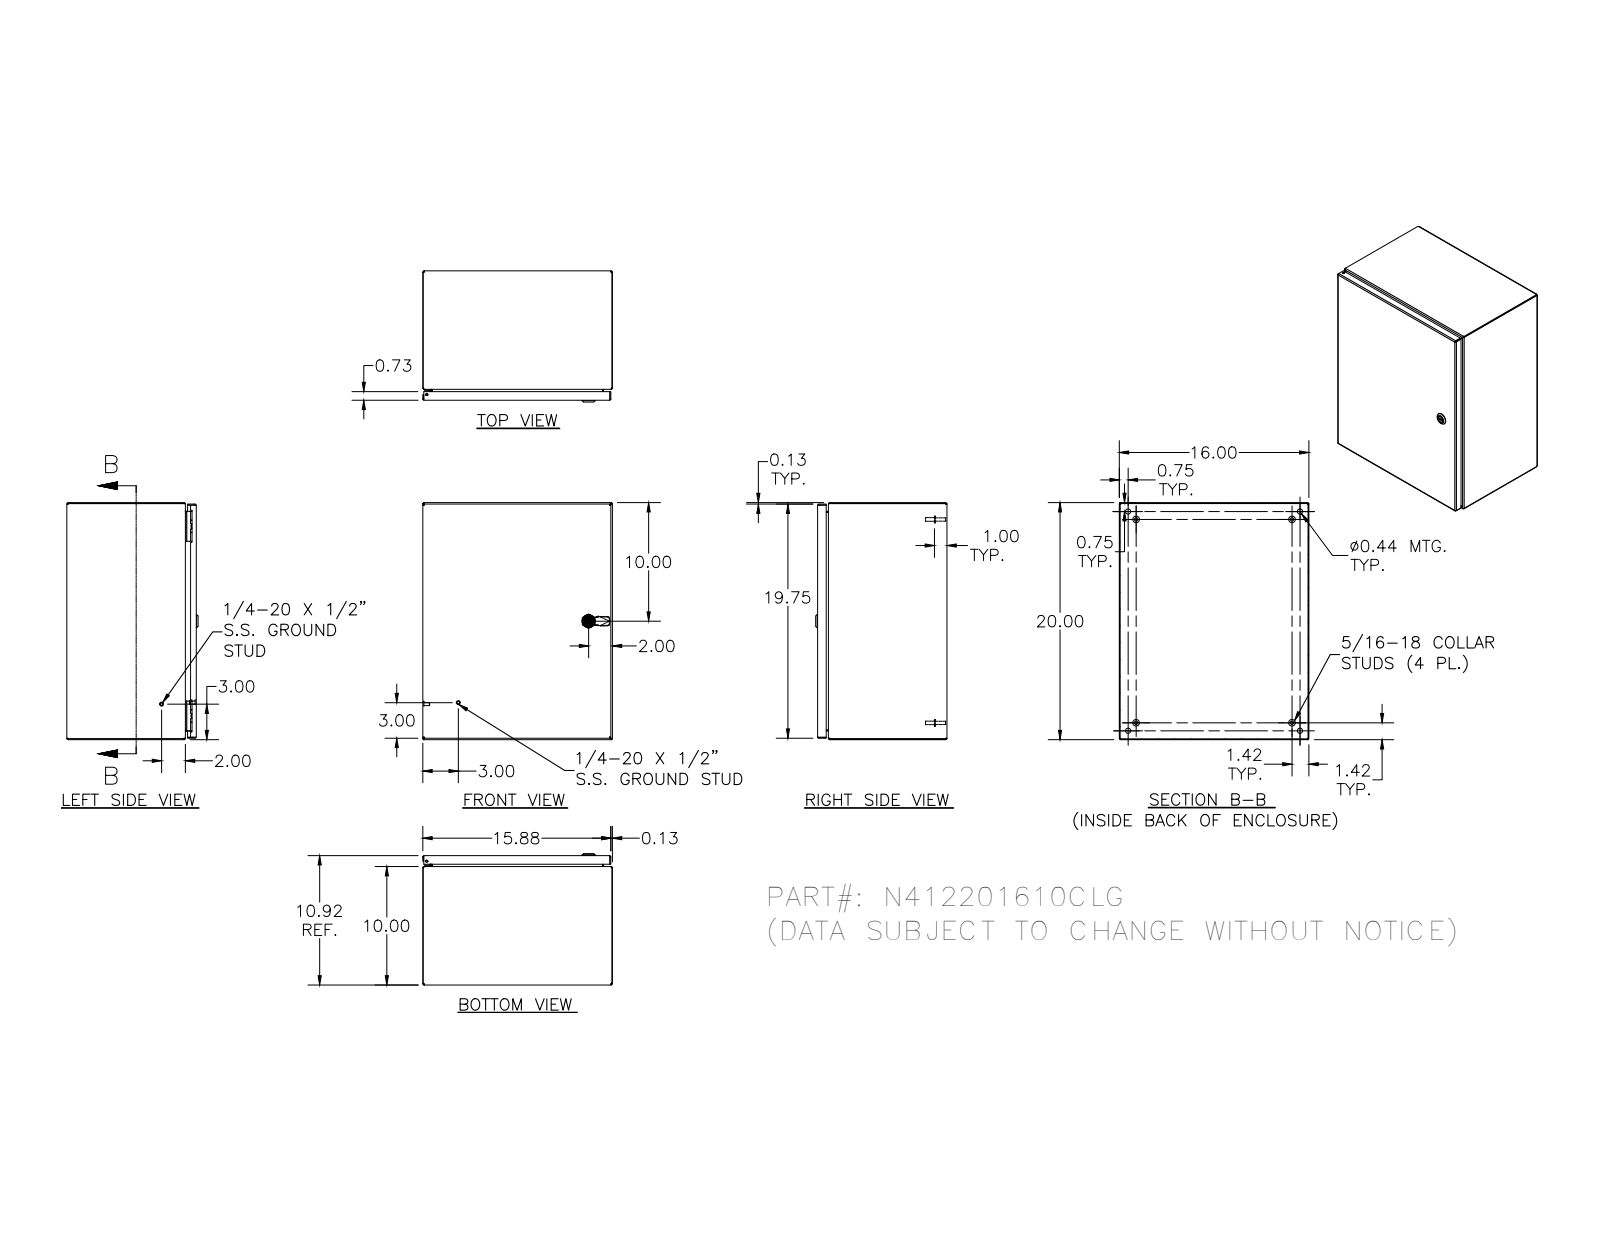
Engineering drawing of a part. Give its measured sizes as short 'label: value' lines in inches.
name: N412201610CLG
written by: SolidWorks 2018 (AUTOMOTIVE_DESIGN)
unit: in
bodies: 33 solids, 1449 faces (530 planar, 547 cylindrical, 372 other)
size: 20 × 16 × 11.075
volume: 111.6 in³; area: 3 034 in²
holes: 5× ⌀0.188, 4× ⌀0.093, 4× ⌀0.152, 4× ⌀0.167, 4× ⌀0.172, 4× ⌀0.437, 2× ⌀0.156, 1× ⌀0.187, 1× ⌀0.197, 1× ⌀0.315, 1× ⌀0.394, 1× ⌀0.402
bosses: 10× ⌀0.25, 5× ⌀0.131, 4× ⌀0.563, 4× ⌀0.36, 4× ⌀0.32, 4× ⌀0.3, 4× ⌀0.275, 4× ⌀0.256
rounds: 30× R0.012, 30× R0.031, 26× R0.05, 20× R0.105, 18× R0.016, 16× R0.125, 13× R0.02, 8× R0.032
face distances: 0.074, 10.843, 0.074, 10.769, 10.917, 15.926, 16, 15.852, 15.926, 19.926
hole spacings: 16, 0.66, 0.656, 1.307, 1.965, 15.34, 15.996, 16.656
